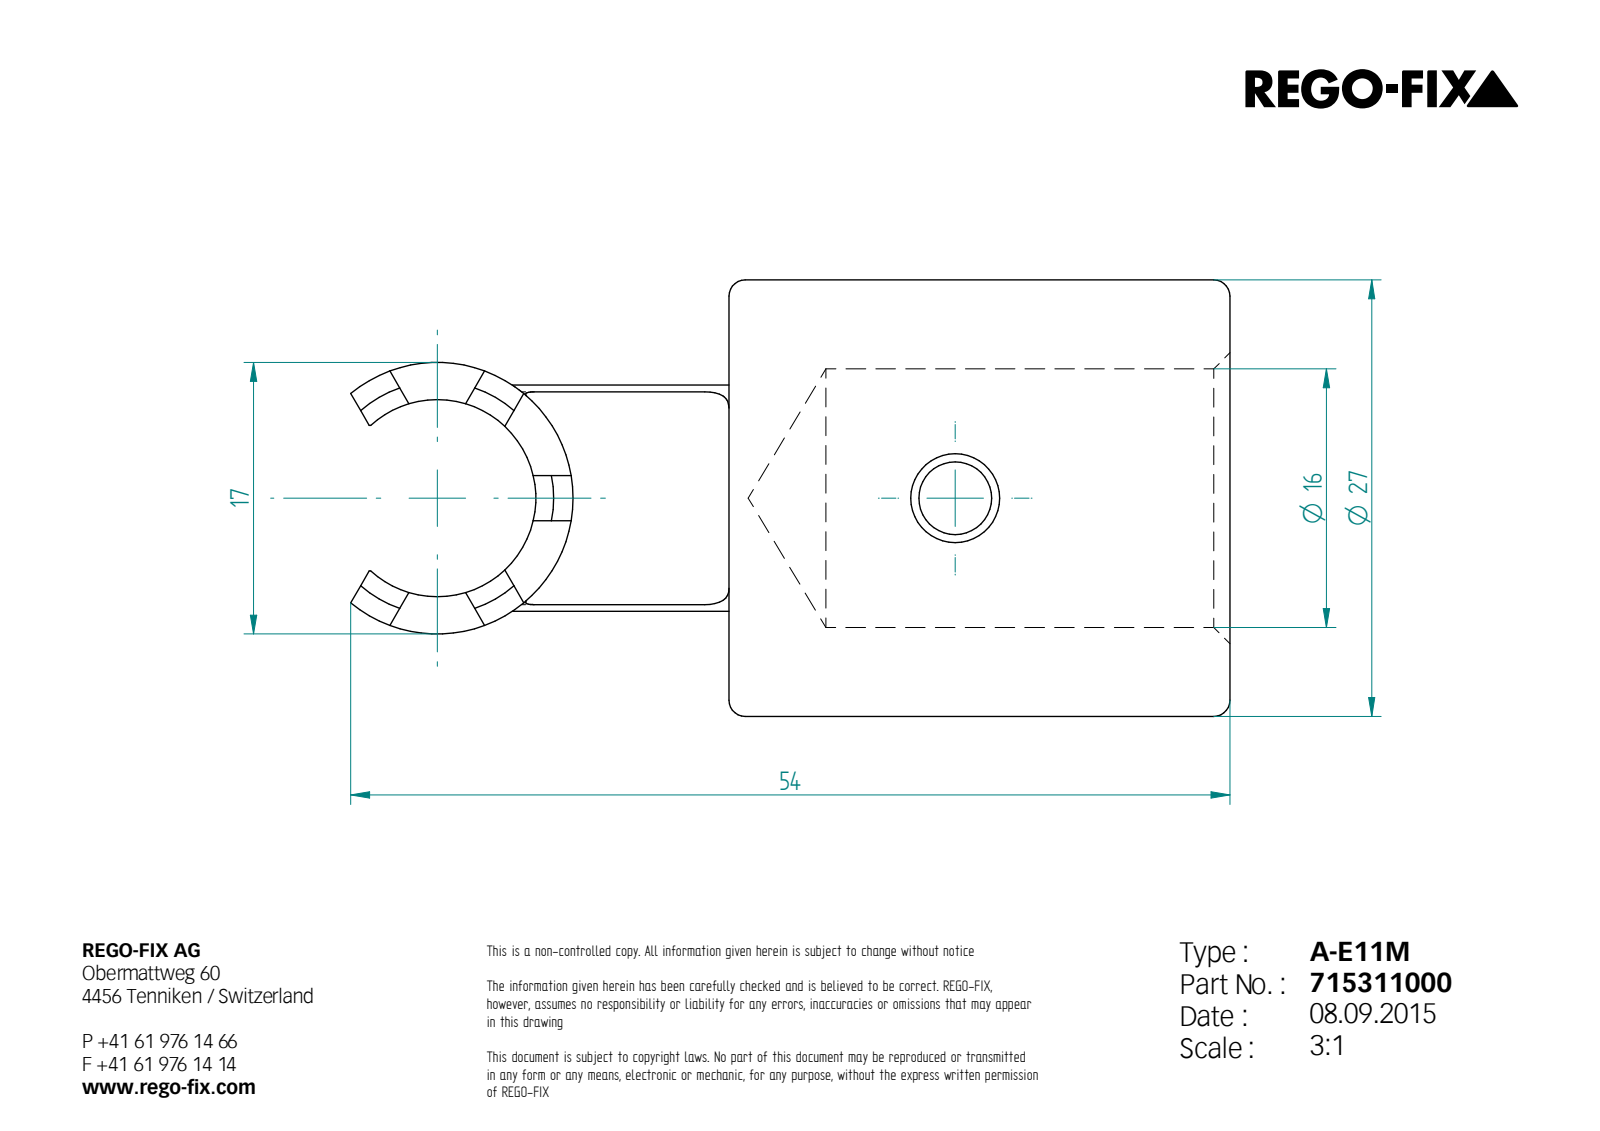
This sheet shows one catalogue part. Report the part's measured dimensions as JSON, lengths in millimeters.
{"step_written_by": "Unknown (AUTOMOTIVE_DESIGN)", "units": "millimeters", "bodies": {"solids": 1, "faces": 47, "planar": 25, "cylindrical": 11, "other": 11}, "overall_size": [54.4, 27, 27], "volume_mm3": 13280, "surface_area_mm2": 6089, "round_holes": [[4.5, 1], [5.5, 1], [16, 1]], "round_bosses_or_shafts": [[27, 1]], "partial_cylinders_radius": [[1.5, 2], [5, 2], [6.1, 1], [8.4, 1]], "face_to_face_distances": [31, 4, 6.7, 2.7, 2.8, 10, 6, 3.3, 3.1, 5.9]}
